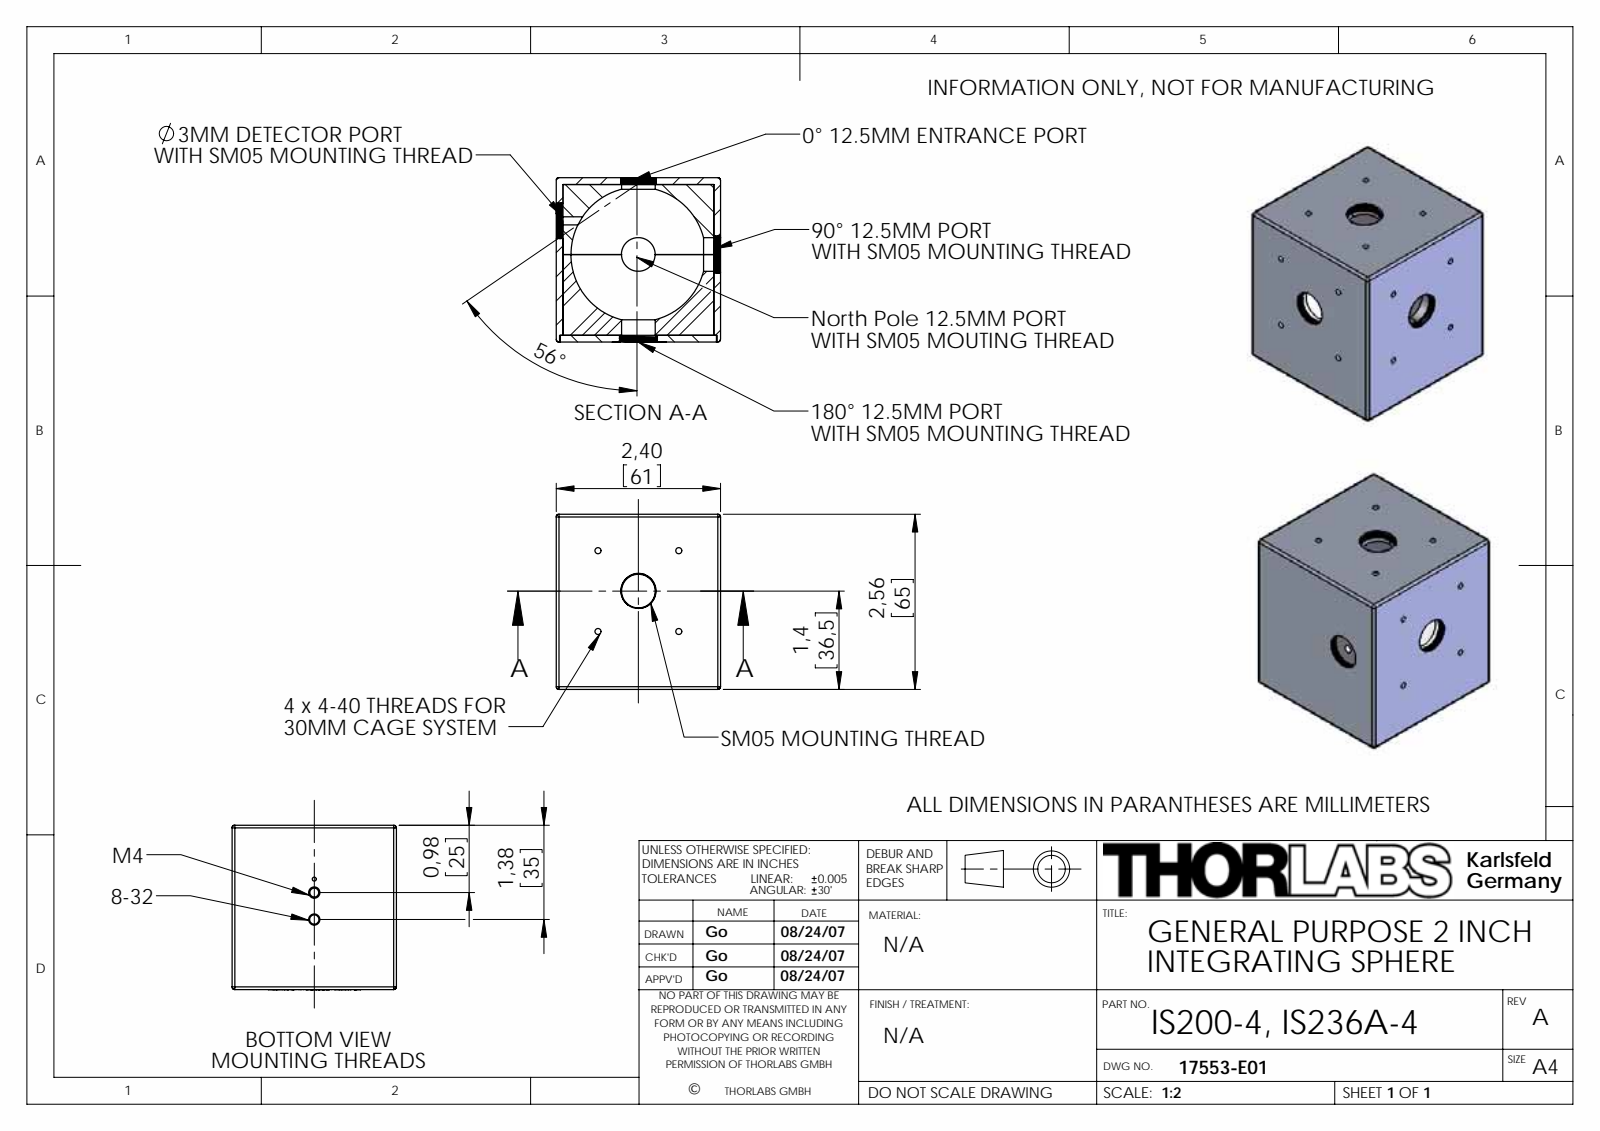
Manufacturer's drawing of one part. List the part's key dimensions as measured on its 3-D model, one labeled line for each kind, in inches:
Part name (STEP PRODUCT): Sphere2Inch_Teil2-4Port; Countersunk Flat Head Cross Recess Screw_DIN_ISO 7046-1 - M2.5 x 8 - Z --- 8N; Cover2inch 4port; SM05L05-Solidworks (+3 more)
STEP written by: SolidWorks 2014 (CONFIG_CONTROL_DESIGN)
Units: inches
Bodies: 10 solids, 1287 faces (890 planar, 153 cylindrical, 244 other)
Overall size (bounding box): 2.931 × 2.559 × 2.404
Volume: 13.5 in³ · Surface area: 129.2 in²
Round holes (diameter × count): ⌀0.089 ×12, ⌀0.081 ×4, ⌀0.114 ×4, ⌀0.492 ×3, ⌀0.118 ×1, ⌀0.13 ×1, ⌀0.136 ×1, ⌀0.45 ×1, ⌀0.508 ×1, ⌀0.535 ×1, ⌀0.565 ×1
Round bosses / shafts (diameter × count): ⌀0.185 ×4, ⌀0.098 ×4, ⌀0.7 ×1, ⌀0.535 ×1, ⌀0.505 ×1
Partial cylindrical surfaces — rounded edges, fillets, slot ends (radius × count): R0.039 ×20, R0.177 ×8, R1.28 ×1
Main face-to-face distances: 0.098, 2.303, 2.205, 2.402, 2.126, 2.224, 0.335, 2.461, 2.559, 1.024
Hole centre spacings: 1.181, 0.835, 1.67, 1.683, 0.573, 0.599, 0.626, 0.699
